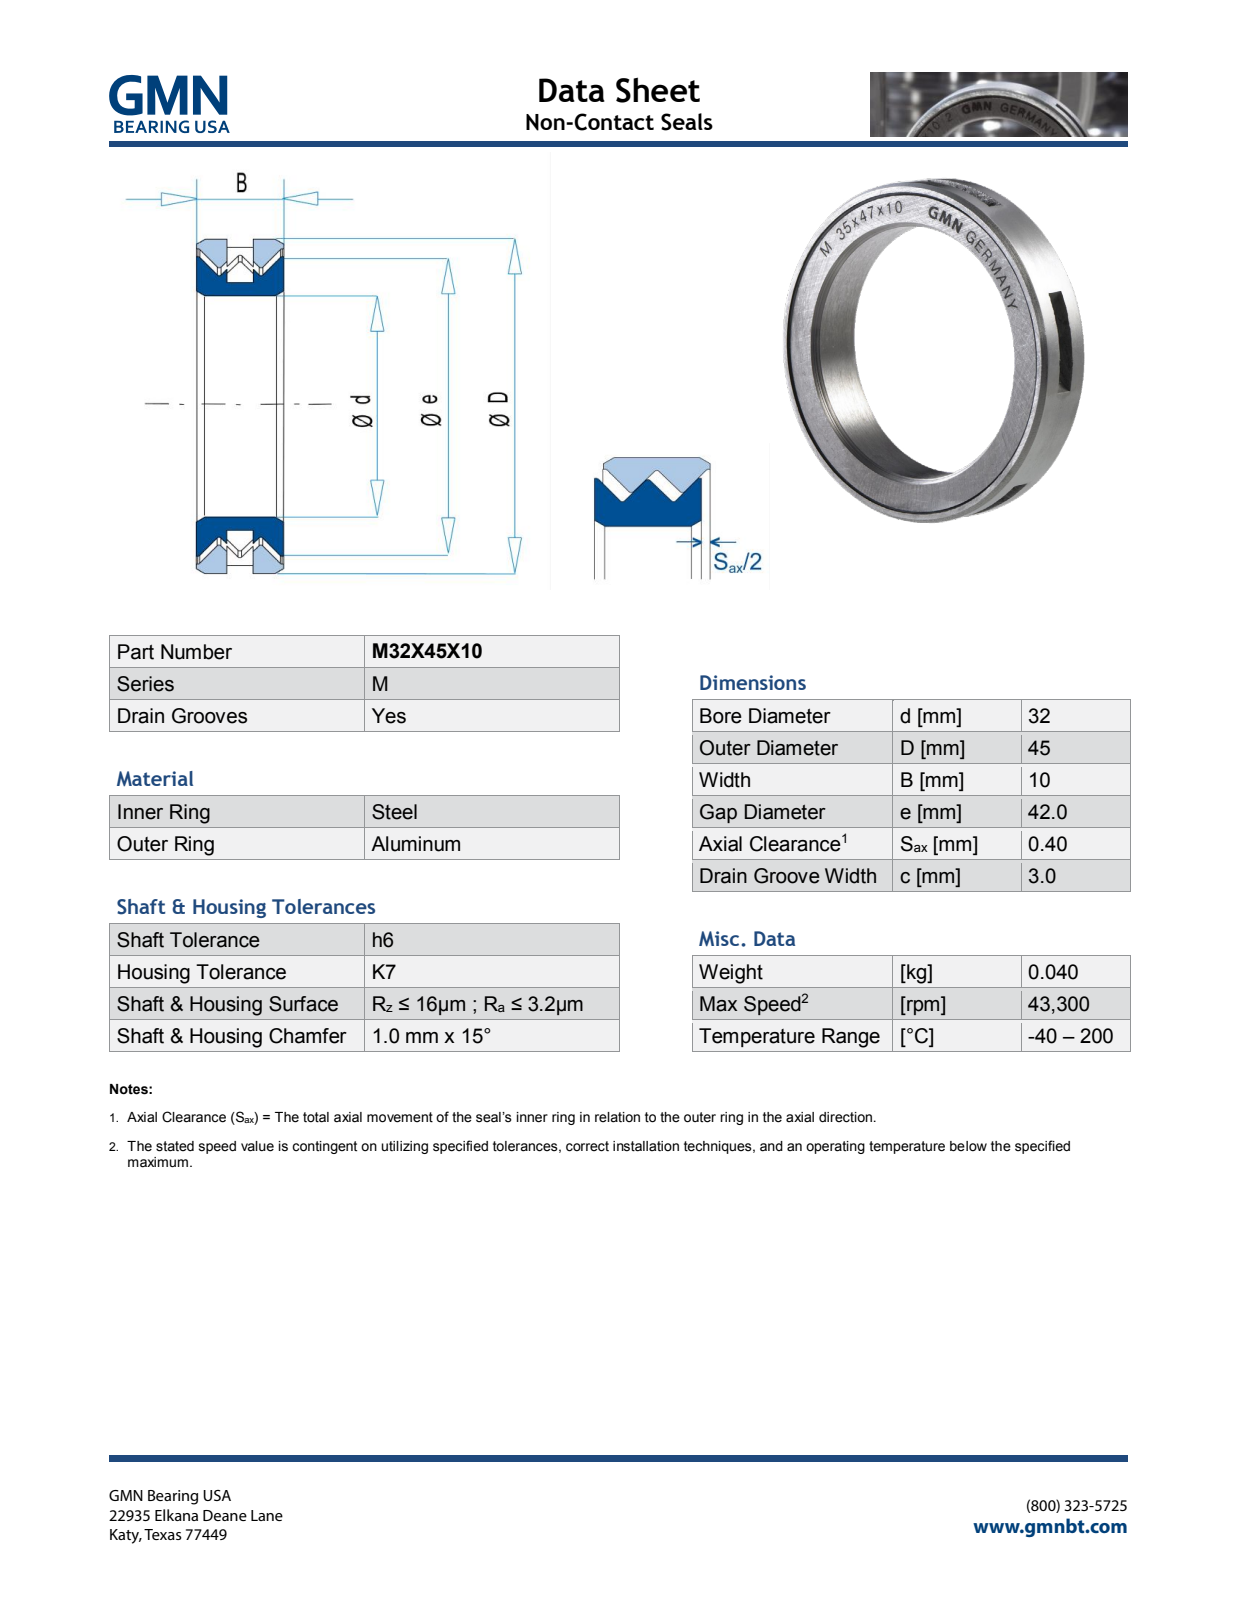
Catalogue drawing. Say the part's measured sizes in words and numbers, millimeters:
The part is named "M32X45X10_PRT". Its 3-D file was written by "PRO/ENGINEER BY PARAMETRIC TECHNOLOGY CORPORATION, 2013150 (AUTOMOTIVE_DESIGN)". It is 2 solids with 595 faces: 528 planar, 21 cylindrical and 46 other. Overall it measures 45 by 45 by 10.07 millimeters. Its volume is 7 030 cubic millimeters and its surface area 7 158 square millimeters. Round holes: 1 of diameter 32, 1 of diameter 42.28. Round bosses or shafts: 1 of diameter 45, 1 of diameter 42. Partial cylindrical surfaces (rounded edges, fillets, slot ends): 3 of radius 10. The main face-to-face distances are 10, 3.5, 6.5, 3, 10.07, 3.57, 6.57, 2.42, 2.12, 0.31.
